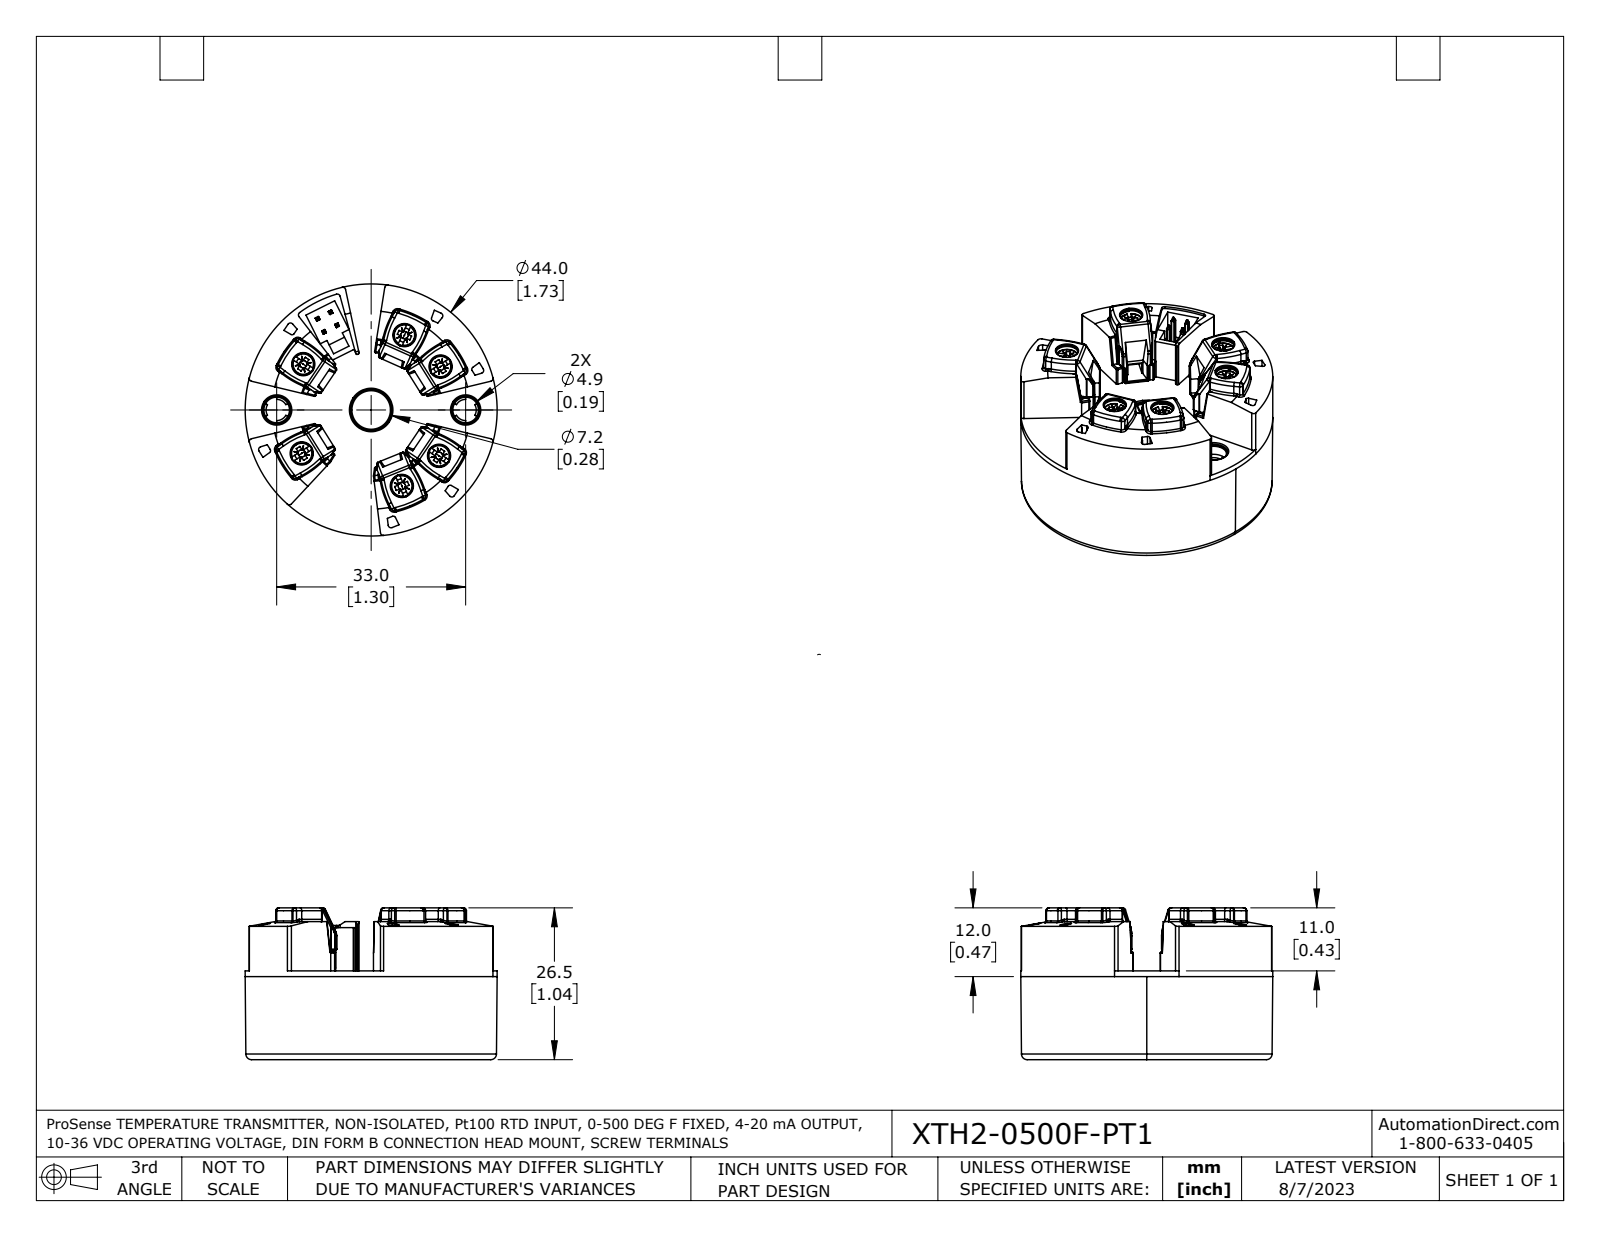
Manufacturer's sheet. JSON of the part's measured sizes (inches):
{"part_name": "XTH2-0500F-PT1", "step_written_by": "SolidWorks 2021 (AUTOMOTIVE_DESIGN)", "units": "inches", "bodies": {"solids": 1, "faces": 2500, "planar": 944, "cylindrical": 967, "other": 589}, "overall_size": [1.732, 1.732, 1.043], "volume_in3": 0.846, "surface_area_in2": 24.66, "round_holes": [[0.102, 6], [0.151, 6], [0.159, 6], [0.193, 2], [0.248, 2], [0.213, 1], [0.283, 1], [0.339, 1], [0.685, 1]], "round_bosses_or_shafts": [[0.106, 12], [0.156, 6], [0.098, 6], [1.732, 1], [1.646, 1], [0.402, 1]], "partial_cylinders_radius": [[0.008, 247], [0.02, 144], [0.012, 58], [0.004, 48], [0.01, 36], [0.006, 18], [0.016, 12], [0.592, 12]], "face_to_face_distances": [0.039, 0.571, 0.453, 0.118, 0.492, 0.61, 0.079, 0.531, 0.098, 0.067], "hole_center_spacings": [0.563, 0.863, 0.329, 0.344, 0.364, 0.563, 0.613, 0.65]}
